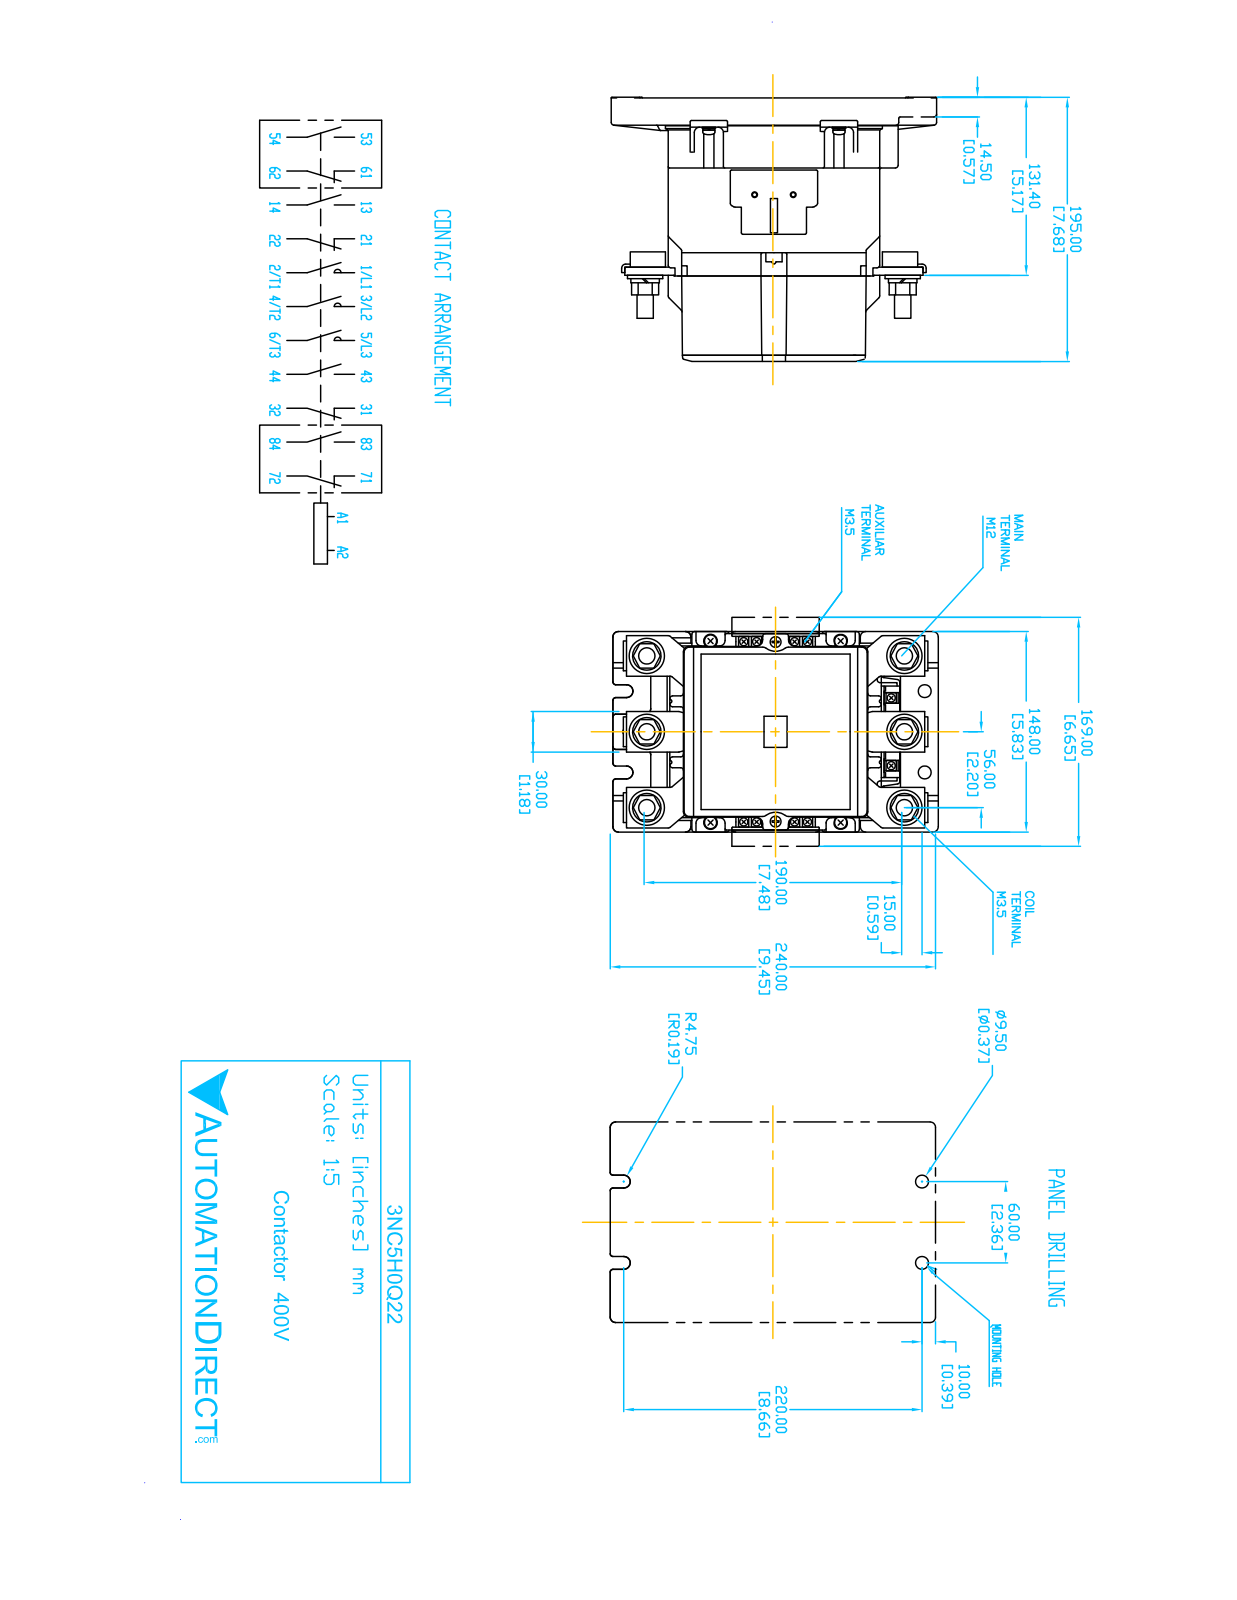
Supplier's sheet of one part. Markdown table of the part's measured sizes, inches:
| quantity | value |
| --- | --- |
| part name | 3NC5H0Q22 |
| STEP written by | SolidWorks 2018 (AUTOMOTIVE_DESIGN) |
| units | inches |
| bodies | 20 solids, 375 faces (261 planar, 114 cylindrical, 0 other) |
| overall size | 9.449 × 7.677 × 5.866 |
| volume | 256.1 in³ |
| surface area | 431.1 in² |
| round holes (diameter × count) | 0.472 × 6, 0.315 × 2, 0.394 × 2 |
| partial cylindrical surfaces (radius × count) | 0.079 × 26, 0.157 × 16, 0.039 × 12, 0.031 × 8, 0.197 × 6, 0.02 × 2 |
| main face-to-face distances | 4.528, 0.433, 4.961, 0.394, 5.748, 5.394, 3.15, 7.677, 0.827, 3.701 |
| hole center spacings | 2.244, 3.765, 4.6, 6.181, 7.81, 7.48, 1.213, 1.324 |
